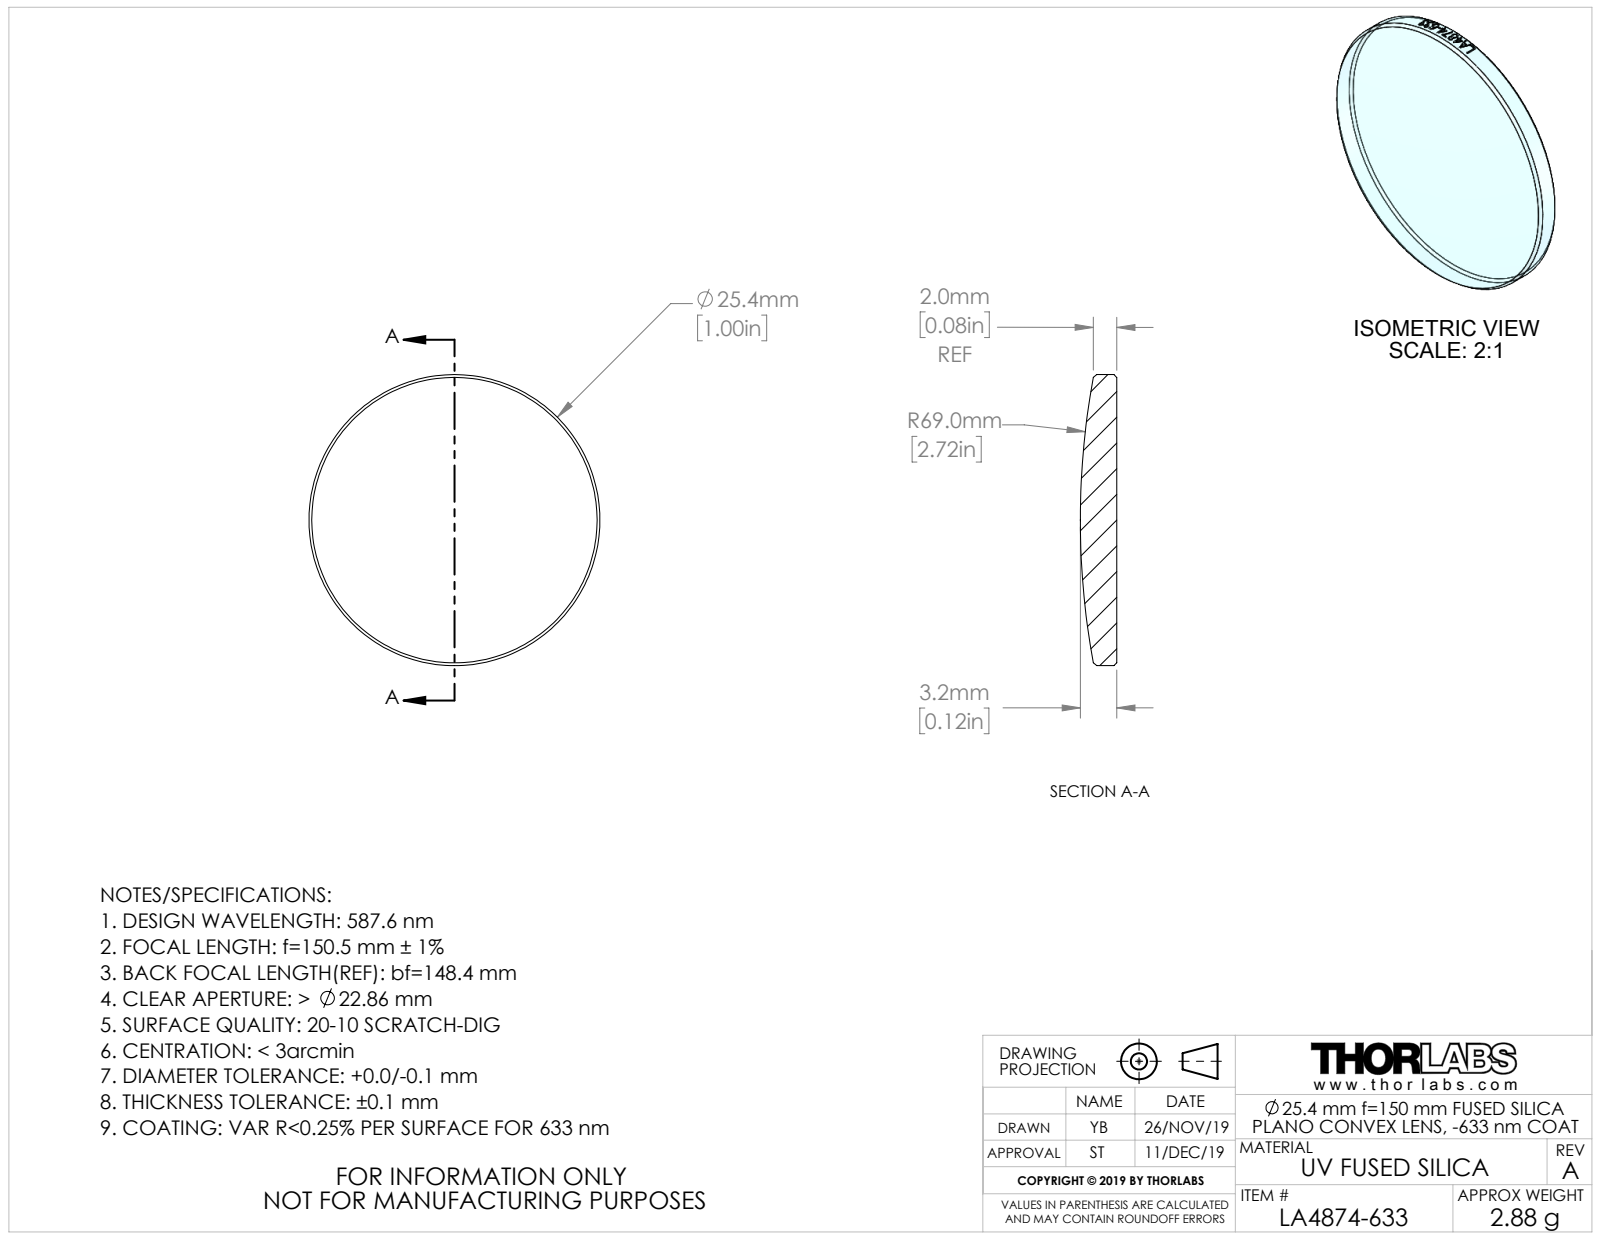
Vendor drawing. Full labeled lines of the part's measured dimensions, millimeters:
Part name (STEP PRODUCT): CTN014985-999; CTN015004
STEP written by: SolidWorks 2018 (AUTOMOTIVE_DESIGN)
Units: millimetres
Bodies: 1 solid, 28 faces (1 planar, 21 cylindrical, 6 other)
Overall size (bounding box): 25.4 × 25.4 × 3.17
Volume: 1 307 mm³ · Surface area: 1 156 mm²
Round bosses / shafts (diameter × count): ⌀25.4 ×1
